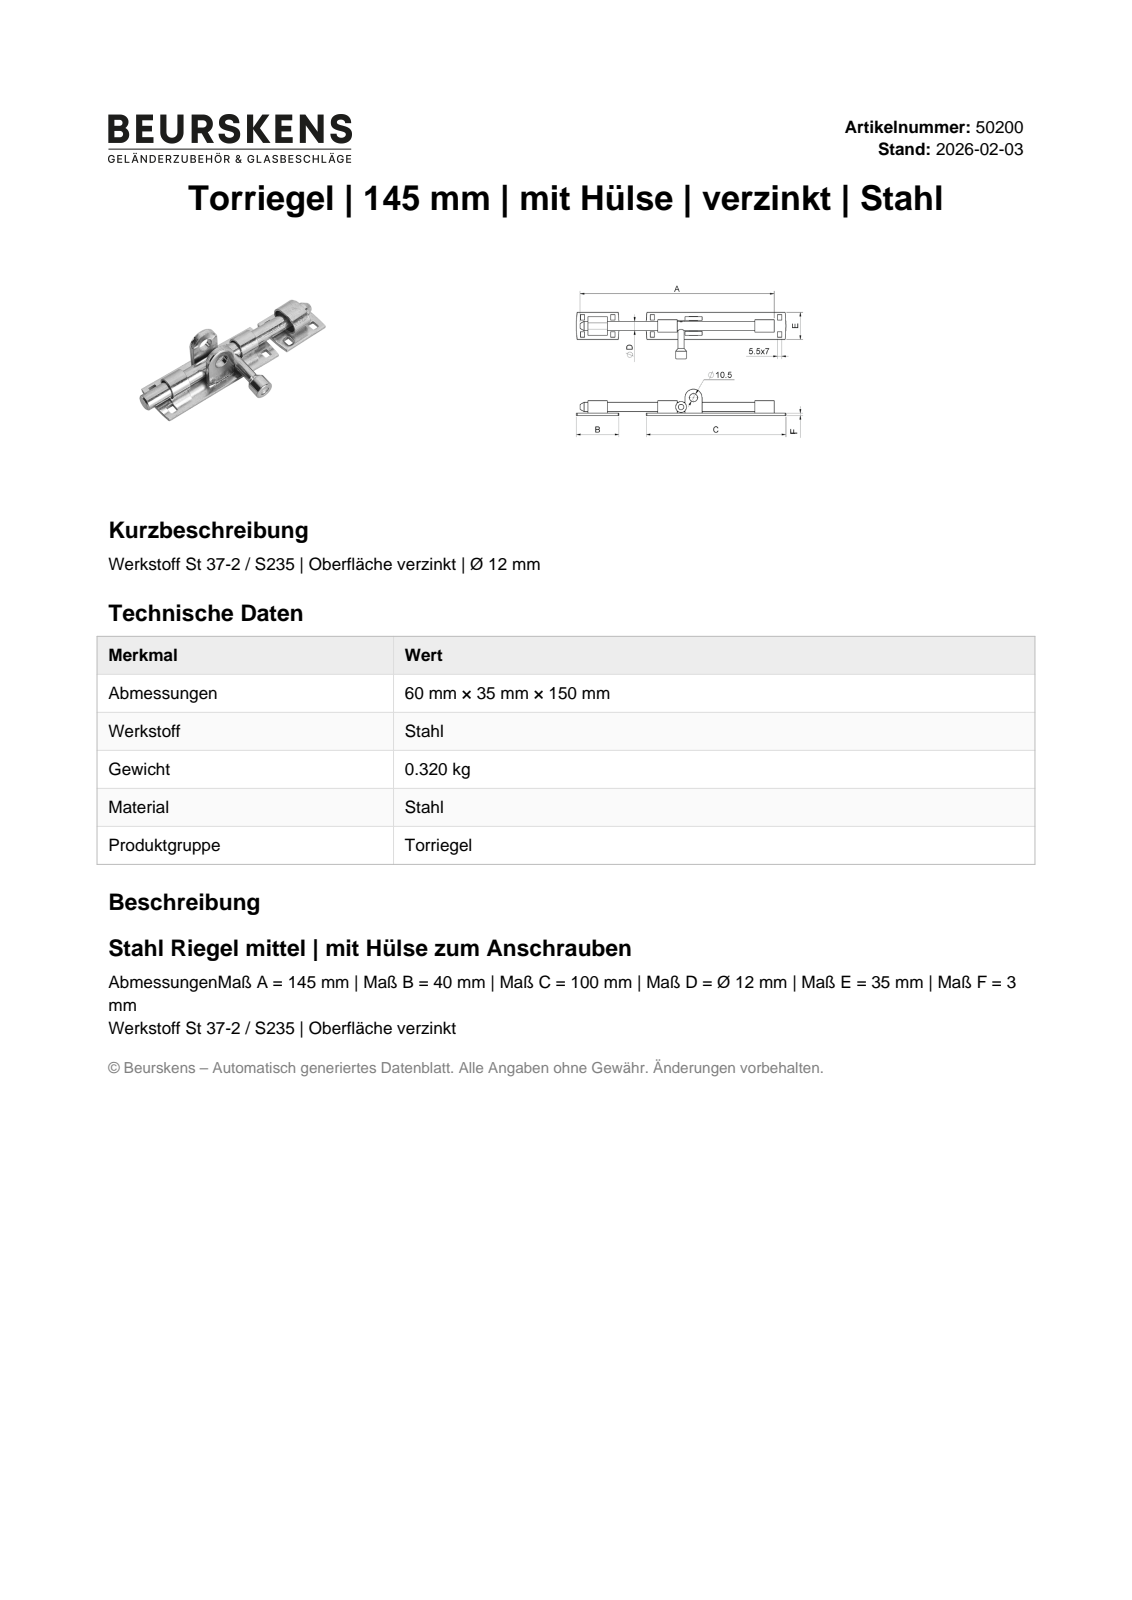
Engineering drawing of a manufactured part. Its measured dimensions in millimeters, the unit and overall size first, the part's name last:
Units: millimetres
Overall size (bounding box): 153 × 49 × 35
Round holes (diameter × count): ⌀10.5 ×1, ⌀12 ×1
Round bosses / shafts (diameter × count): ⌀16 ×1, ⌀14 ×1, ⌀11.95 ×1, ⌀8 ×1
Partial cylindrical surfaces — rounded edges, fillets, slot ends (radius × count): R7 ×2, R9 ×2, R11 ×1
Main face-to-face distances: 3, 5.25, 18.75, 5.5, 29.5, 10.75, 24.25, 24, 35, 13.5
Volume: 42 707 mm³ · Surface area: 25 707 mm²
Bodies: 5 solids, 89 faces (66 planar, 19 cylindrical, 4 other)
Part name (STEP PRODUCT): 50200; 50200 Anbauteil; 50200 Riegel; 50200 Hülse
STEP written by: Autodesk Inventor 2023 (AUTOMOTIVE_DESIGN)
